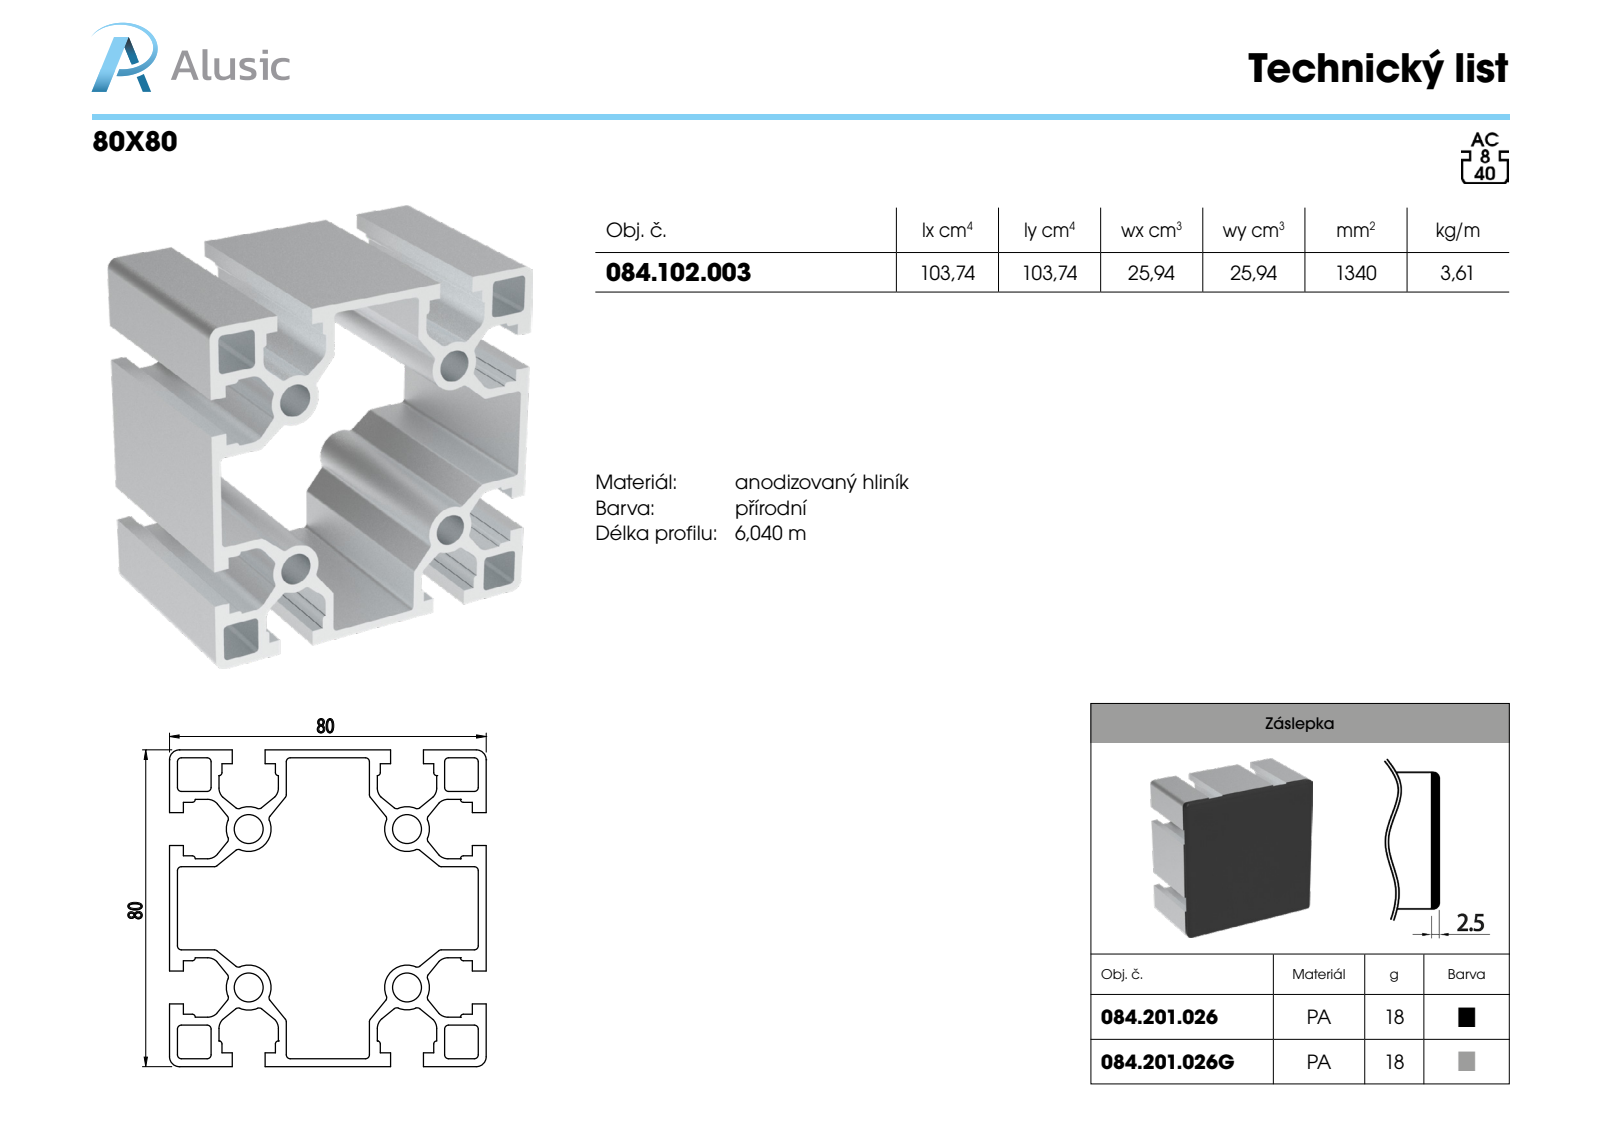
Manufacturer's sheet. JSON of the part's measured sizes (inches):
{"part_name": "084.102.003", "step_written_by": "SolidWorks 2011 (CONFIG_CONTROL_DESIGN)", "units": "inches", "bodies": {"solids": 1, "faces": 252, "planar": 130, "cylindrical": 122, "other": 0}, "overall_size": [3.937, 3.15, 3.15], "volume_in3": 8.135, "surface_area_in2": 175.9, "round_holes": [[0.287, 4]], "partial_cylinders_radius": [[0.039, 56], [0.03, 16], [0.126, 16], [0.222, 5], [0.098, 4]], "face_to_face_distances": [0.079, 3.071, 3.15, 1.575, 1.083, 1.988, 0.413, 2.657, 1.161, 1.909], "hole_center_spacings": [1.575, 2.227]}
